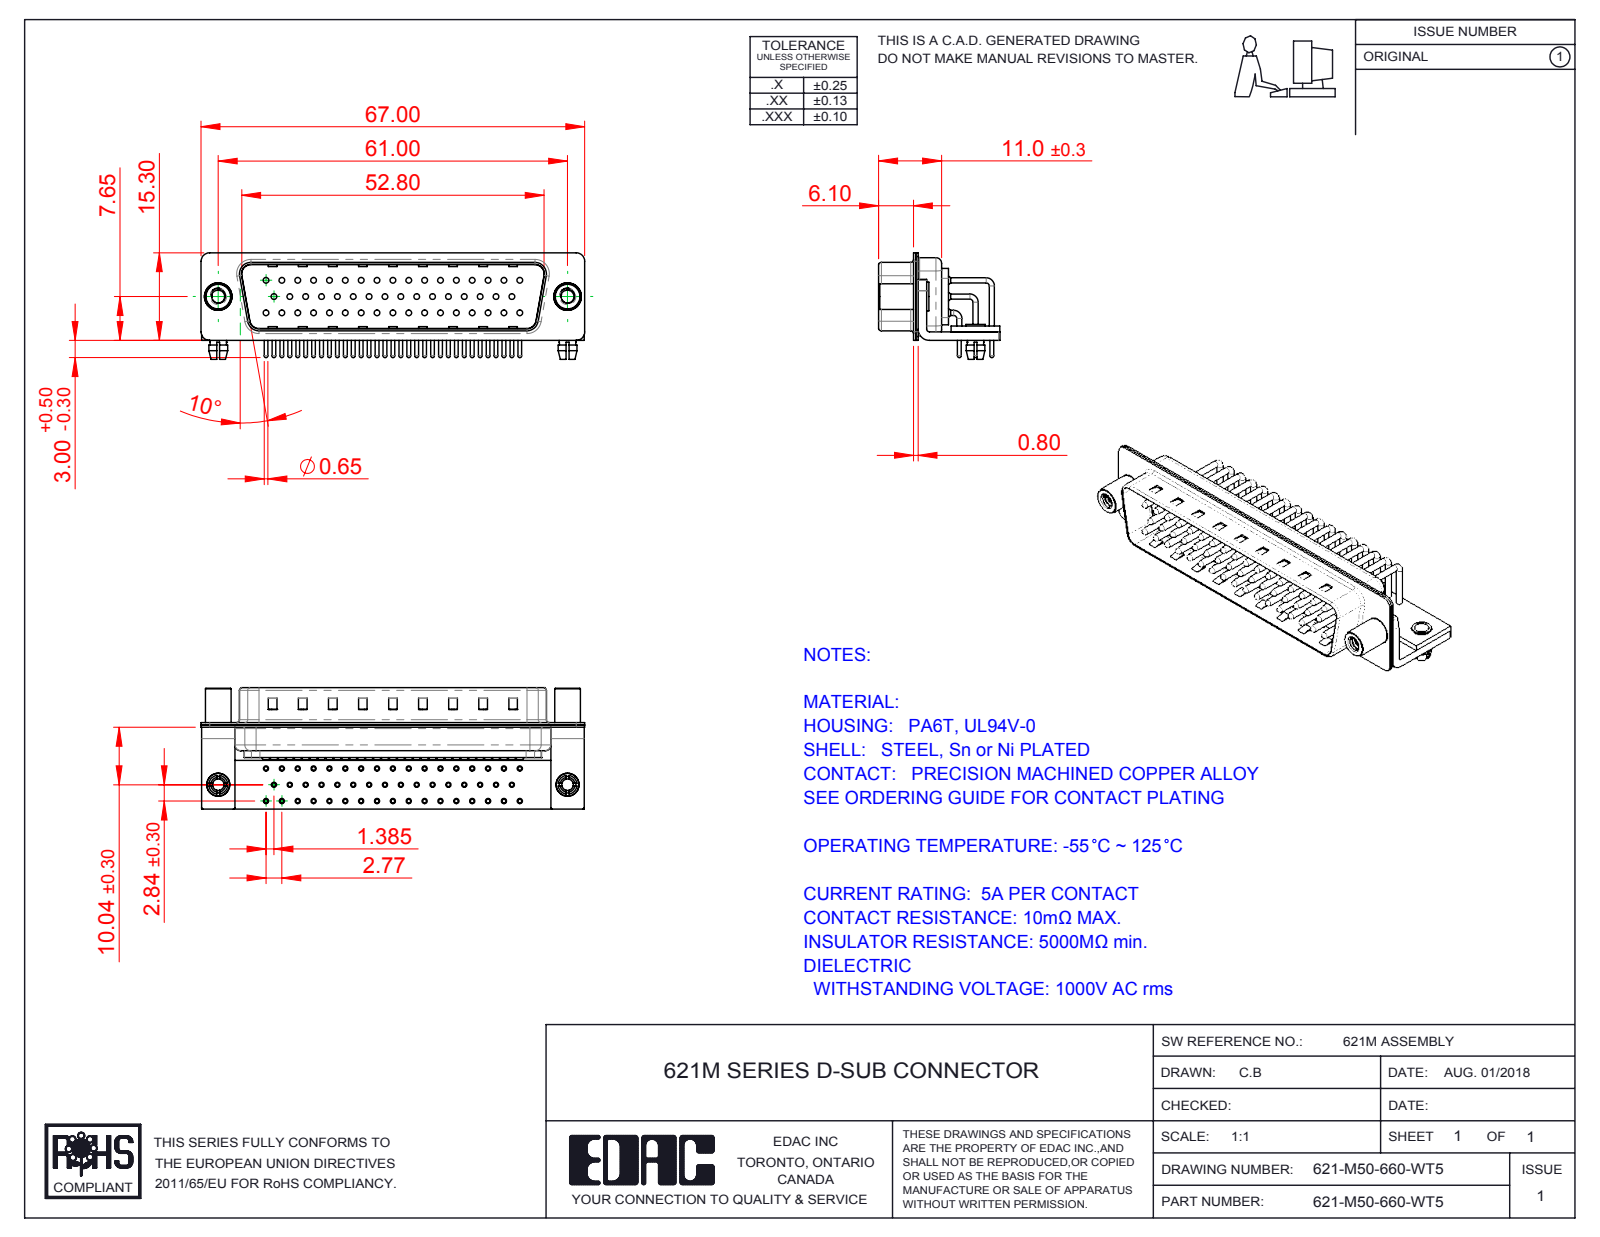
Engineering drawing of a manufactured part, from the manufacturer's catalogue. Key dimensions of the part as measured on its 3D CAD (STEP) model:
Part name (STEP PRODUCT): 621M 4-40 Threaded Standoff; 621M Stabilizer Bracket_50 Contacts; 621M Stabilizer Board_50 Contacts; 621M Contact Row 1_50 Contacts (+7 more)
STEP written by: SolidWorks 2016 (CONFIG_CONTROL_DESIGN)
Units: millimetres
Bodies: 60 solids, 6204 faces (3479 planar, 2137 cylindrical, 588 other)
Overall size (bounding box): 67 × 21.2 × 18.6
Volume: 5 906 mm³ · Surface area: 15 120 mm²
Round holes (diameter × count): ⌀2 ×52, ⌀0.9 ×50, ⌀1 ×50, ⌀1.7 ×50, ⌀2.26 ×2, ⌀2.5 ×2, ⌀3.2 ×2, ⌀4 ×2, ⌀4.8 ×2
Round bosses / shafts (diameter × count): ⌀0.9 ×58, ⌀1.5 ×50, ⌀0.65 ×50, ⌀5 ×2, ⌀4.9 ×2, ⌀4.5 ×2, ⌀4 ×2, ⌀3.4 ×2
Partial cylindrical surfaces — rounded edges, fillets, slot ends (radius × count): R1.01 ×50, R0.25 ×16, R1.5 ×16, R2 ×13, R0.5 ×9, R1.6 ×8, R0.6 ×4, R0.65 ×4
Main face-to-face distances: 0.4, 1, 11.55, 0.83, 1.5, 5.7, 0.43, 11.95, 1.9, 0.8
Hole centre spacings: 2.77, 3.16, 5.54, 8.31, 11.08, 13.85, 16.62, 19.39
